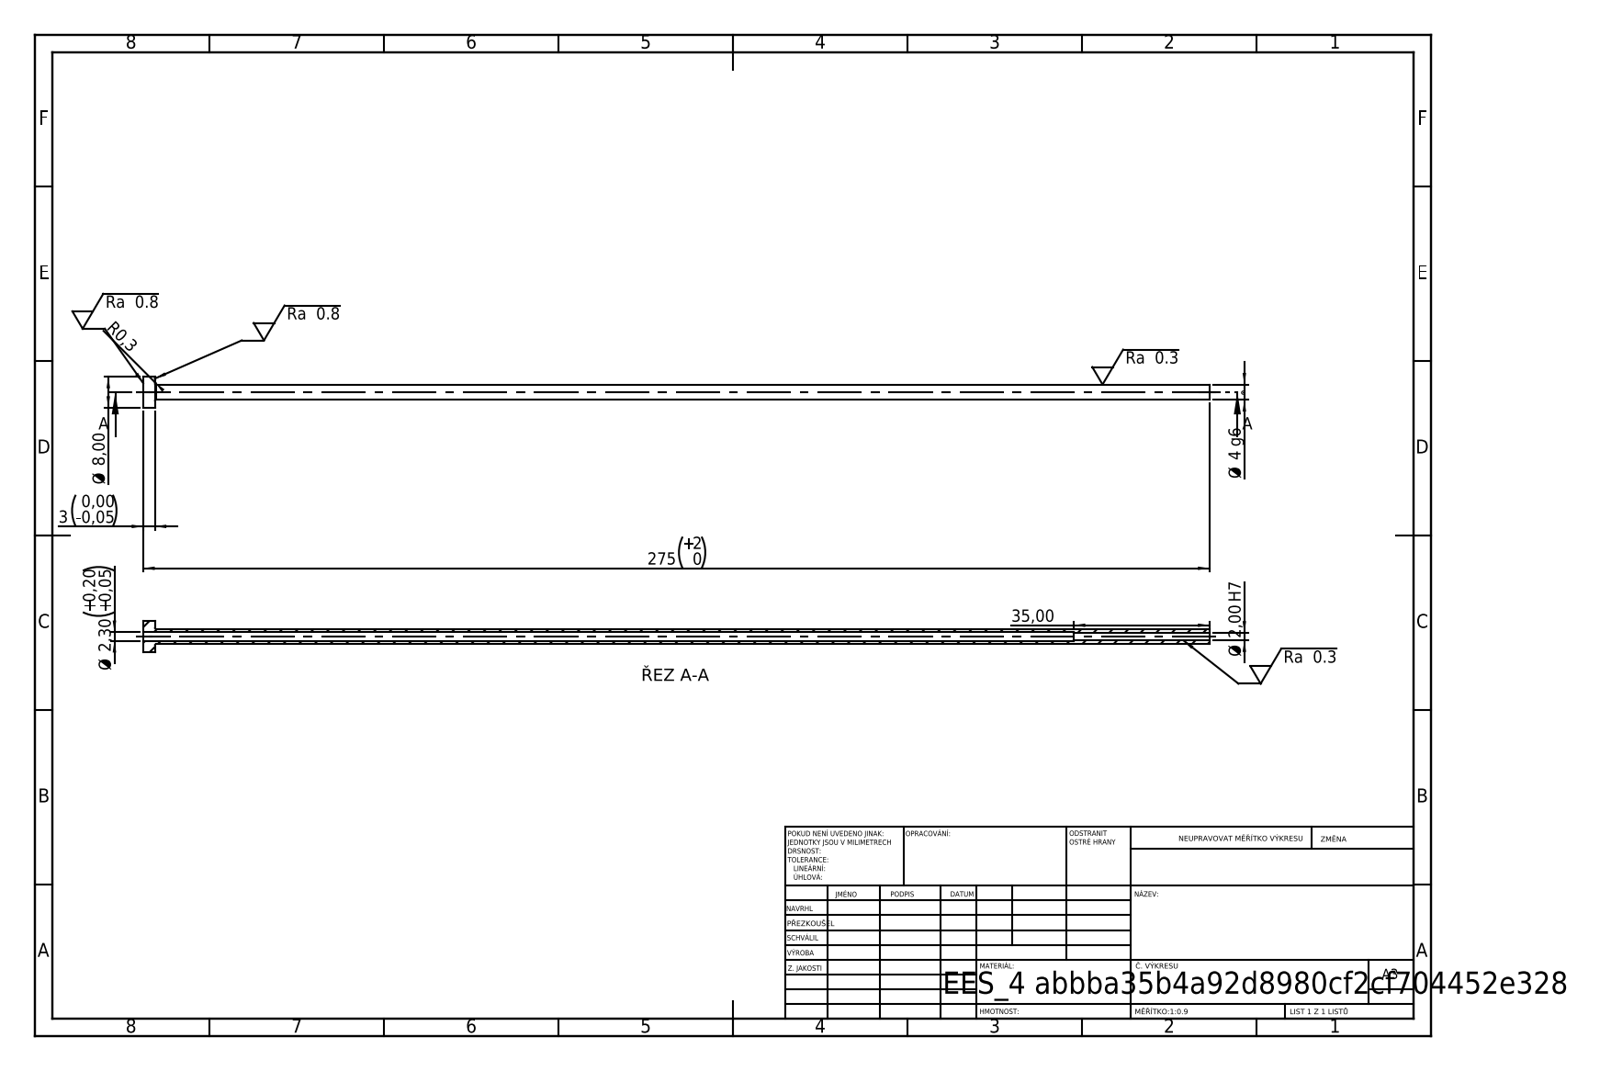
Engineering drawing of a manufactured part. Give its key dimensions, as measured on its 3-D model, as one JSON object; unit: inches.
{"step_written_by": "SolidWorks 2019 (CONFIG_CONTROL_DESIGN)", "units": "inches", "bodies": {"solids": 1, "faces": 14, "planar": 4, "cylindrical": 8, "other": 2}, "overall_size": [10.827, 0.315, 0.315], "volume_in3": 0.15, "surface_area_in2": 8.587, "round_holes": [[0.079, 1], [0.091, 1]], "round_bosses_or_shafts": [[0.315, 1], [0.157, 1]], "face_to_face_distances": [0.118, 10.827, 10.709, 9.449, 9.331, 1.378]}
